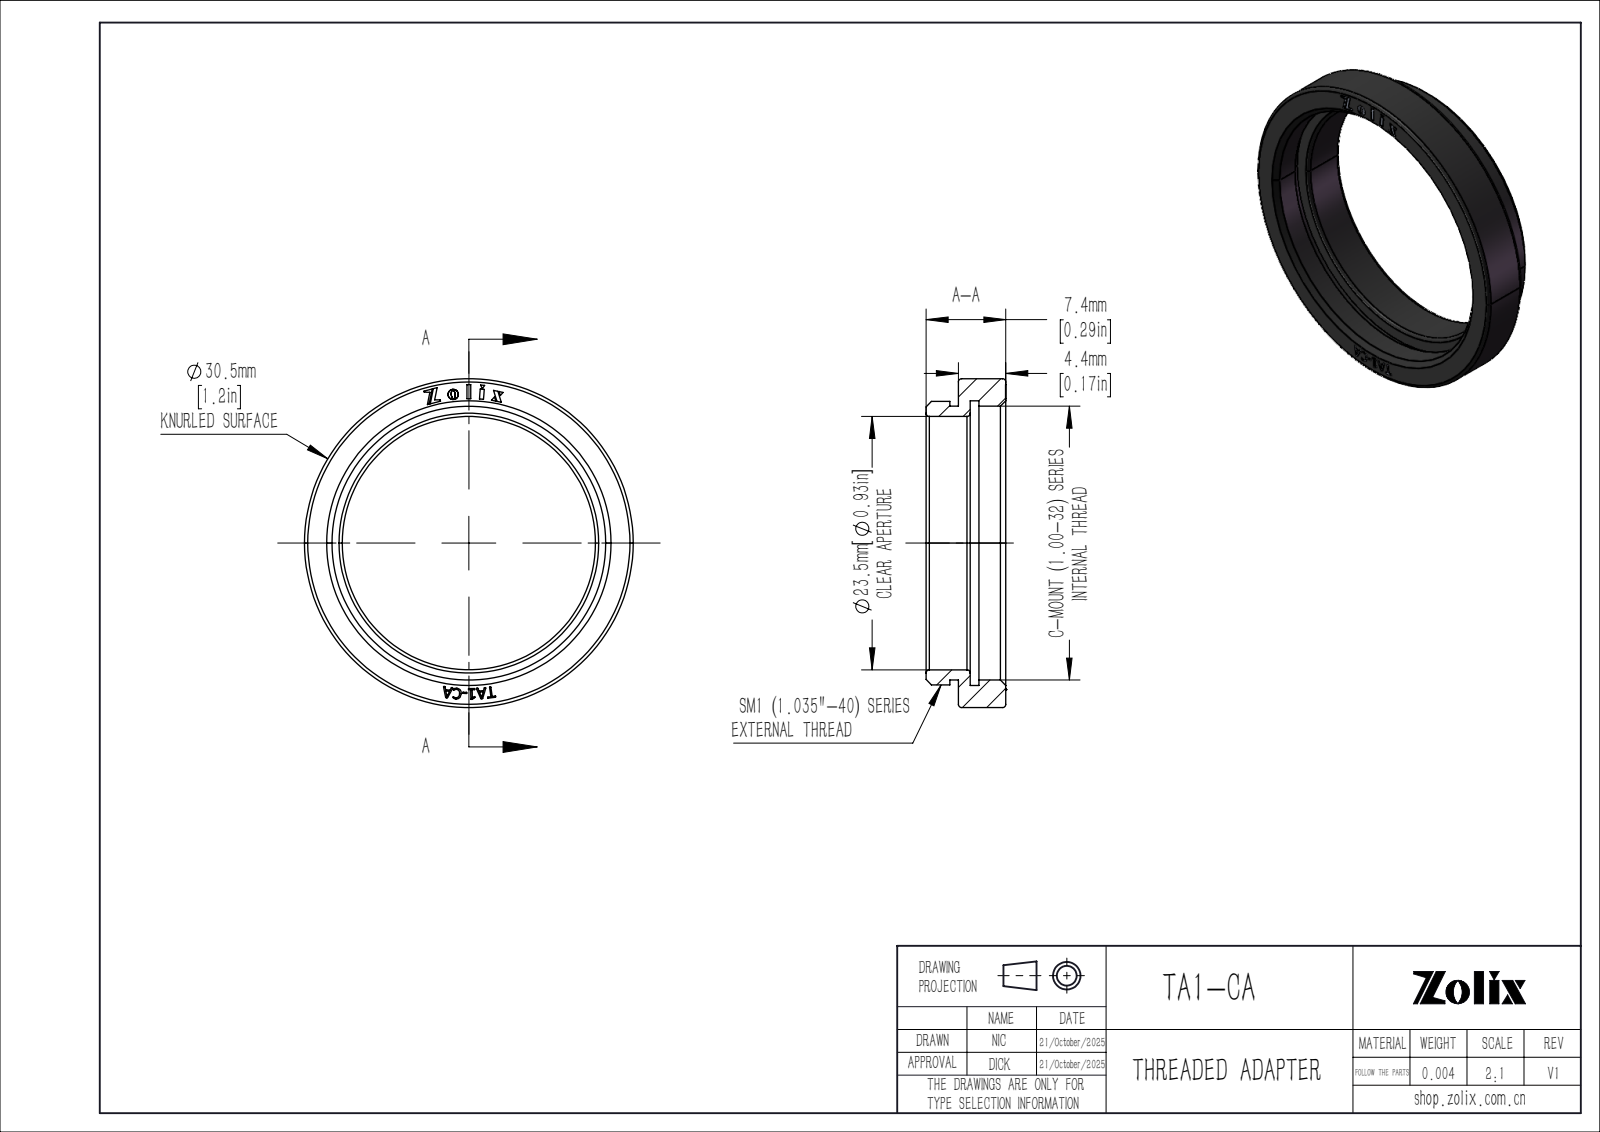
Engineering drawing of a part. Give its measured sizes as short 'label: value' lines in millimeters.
name: TA1-CA
written by: SolidWorks 2020 (CONFIG_CONTROL_DESIGN)
unit: mm
bodies: 1 solid, 271 faces (201 planar, 12 cylindrical, 58 other)
size: 30.5 × 30.5 × 7.4
volume: 1 304 mm³; area: 1 893 mm²
holes: 1× ⌀23.5, 1× ⌀25.4, 1× ⌀26.4
bosses: 1× ⌀30.5, 1× ⌀26.29
face distances: 4.4, 1.1, 3.3, 0.8, 1.9, 3, 4.1, 7.4, 4.9, 2.5
